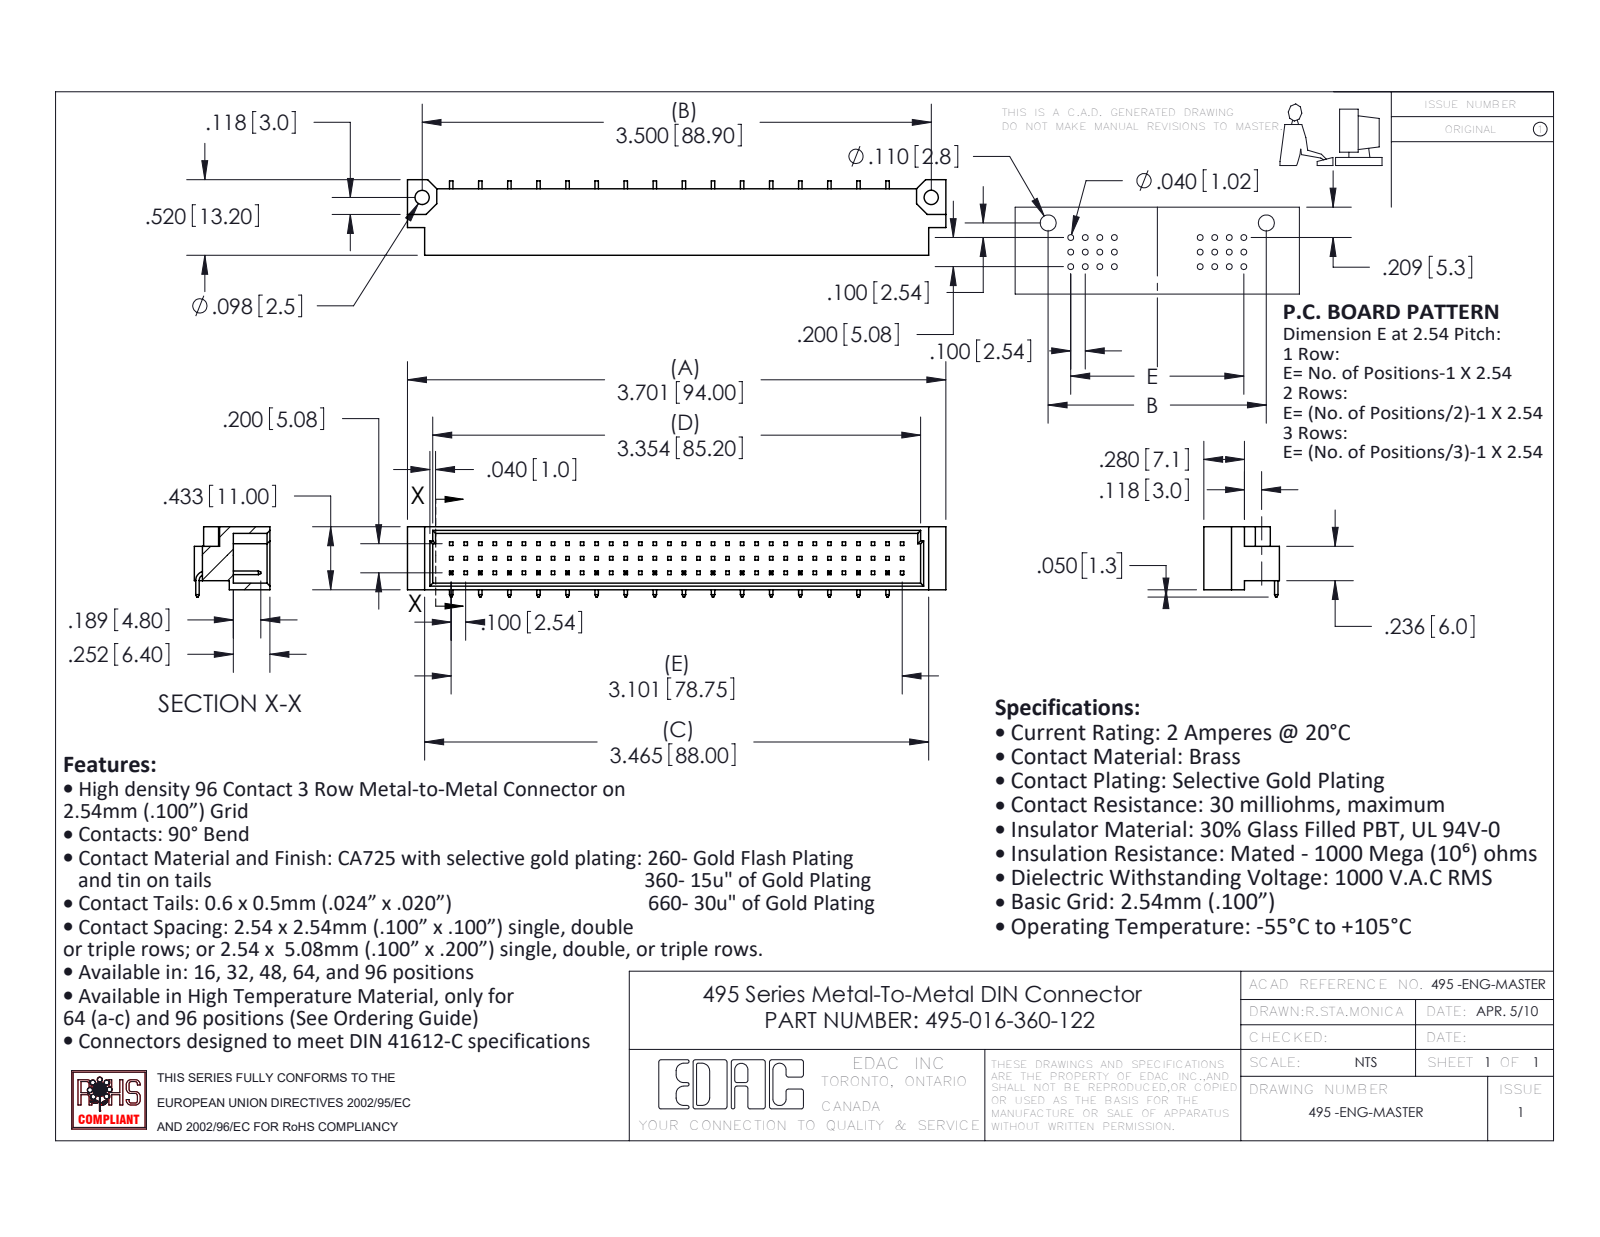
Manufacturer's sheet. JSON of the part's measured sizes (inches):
{"part_name": "495-290-3; 495 Part_96; 495-016-360-122", "step_written_by": "SolidWorks 2020 (AUTOMOTIVE_DESIGN)", "units": "inches", "bodies": {"solids": 17, "faces": 721, "planar": 685, "cylindrical": 36, "other": 0}, "overall_size": [3.701, 0.52, 0.483], "volume_in3": 0.367, "surface_area_in2": 11.49, "round_holes": [[0.098, 2]], "partial_cylinders_radius": [[0.04, 1], [0.065, 1]], "face_to_face_distances": [0.045, 0.388, 0.205, 0.433, 0.343, 0.063, 0.37, 0.018, 0.325, 0.024], "hole_center_spacings": [3.5]}
